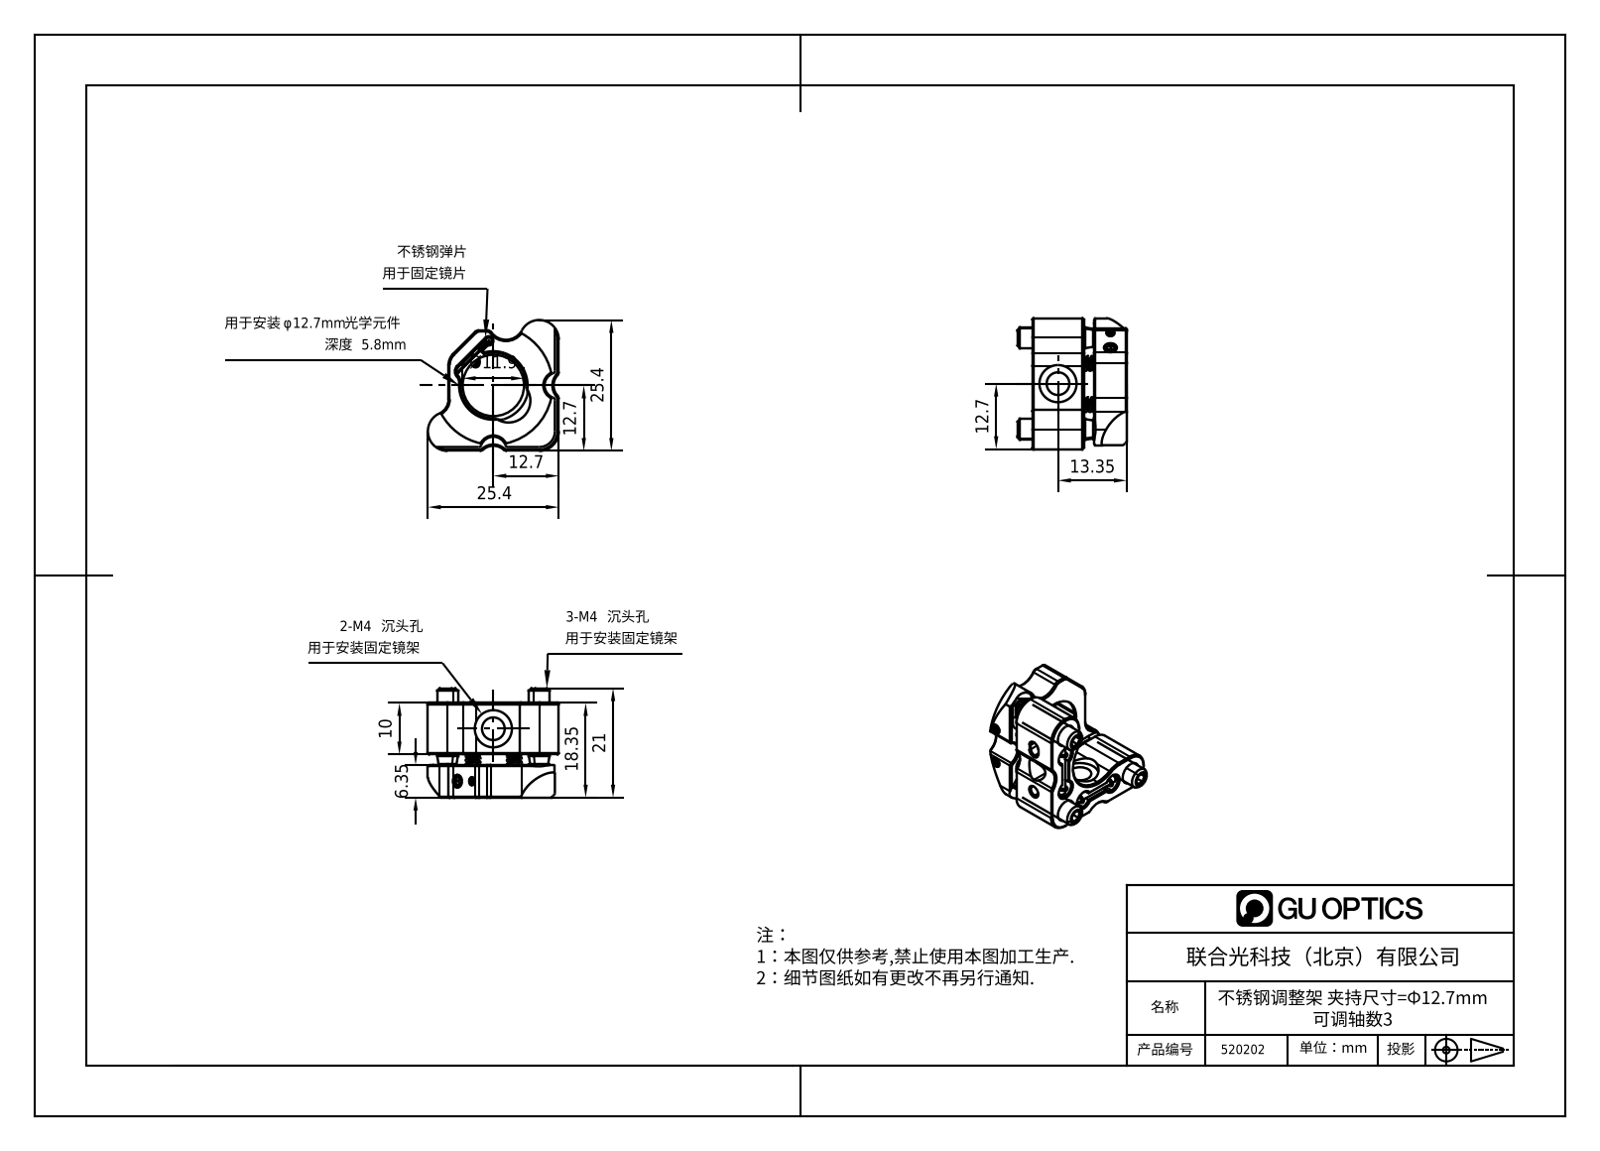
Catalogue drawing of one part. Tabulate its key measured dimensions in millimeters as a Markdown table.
| quantity | value |
| --- | --- |
| part name | 1.1.20.5_ZJO-0.5-3_替代进口不锈钢光学调整架，用于0.5英寸光学原件，顶丝固定，三轴 |
| STEP written by | SolidWorks 2018 (AUTOMOTIVE_DESIGN) |
| units | millimeters |
| bodies | 0 solids, 452 faces (142 planar, 113 cylindrical, 197 other) |
| overall size | 25.4 × 25.4 × 21.22 |
| round holes (diameter × count) | 3.2 × 4, 3.4 × 4, 2 × 2, 4.4 × 2, 7.2 × 2, 1.6 × 1, 2.5 × 1, 11.9 × 1 |
| round bosses / shafts (diameter × count) | 2.6 × 6, 4 × 3, 1.5 × 2, 3 × 1, 2 × 1 |
| partial cylindrical surfaces (radius × count) | 1 × 12, 0.5 × 4, 3 × 4, 2 × 3, 3.81 × 3, 2.5 × 2, 5 × 2, 0.3 × 1 |
| main face-to-face distances | 2, 6.35, 8.35, 18.35, 12, 10, 0.76, 2.5, 7.62, 6.86 |
| hole center spacings | 7.87, 9.72, 9.73, 13.75, 18.14, 7.01, 13.76, 5 |
